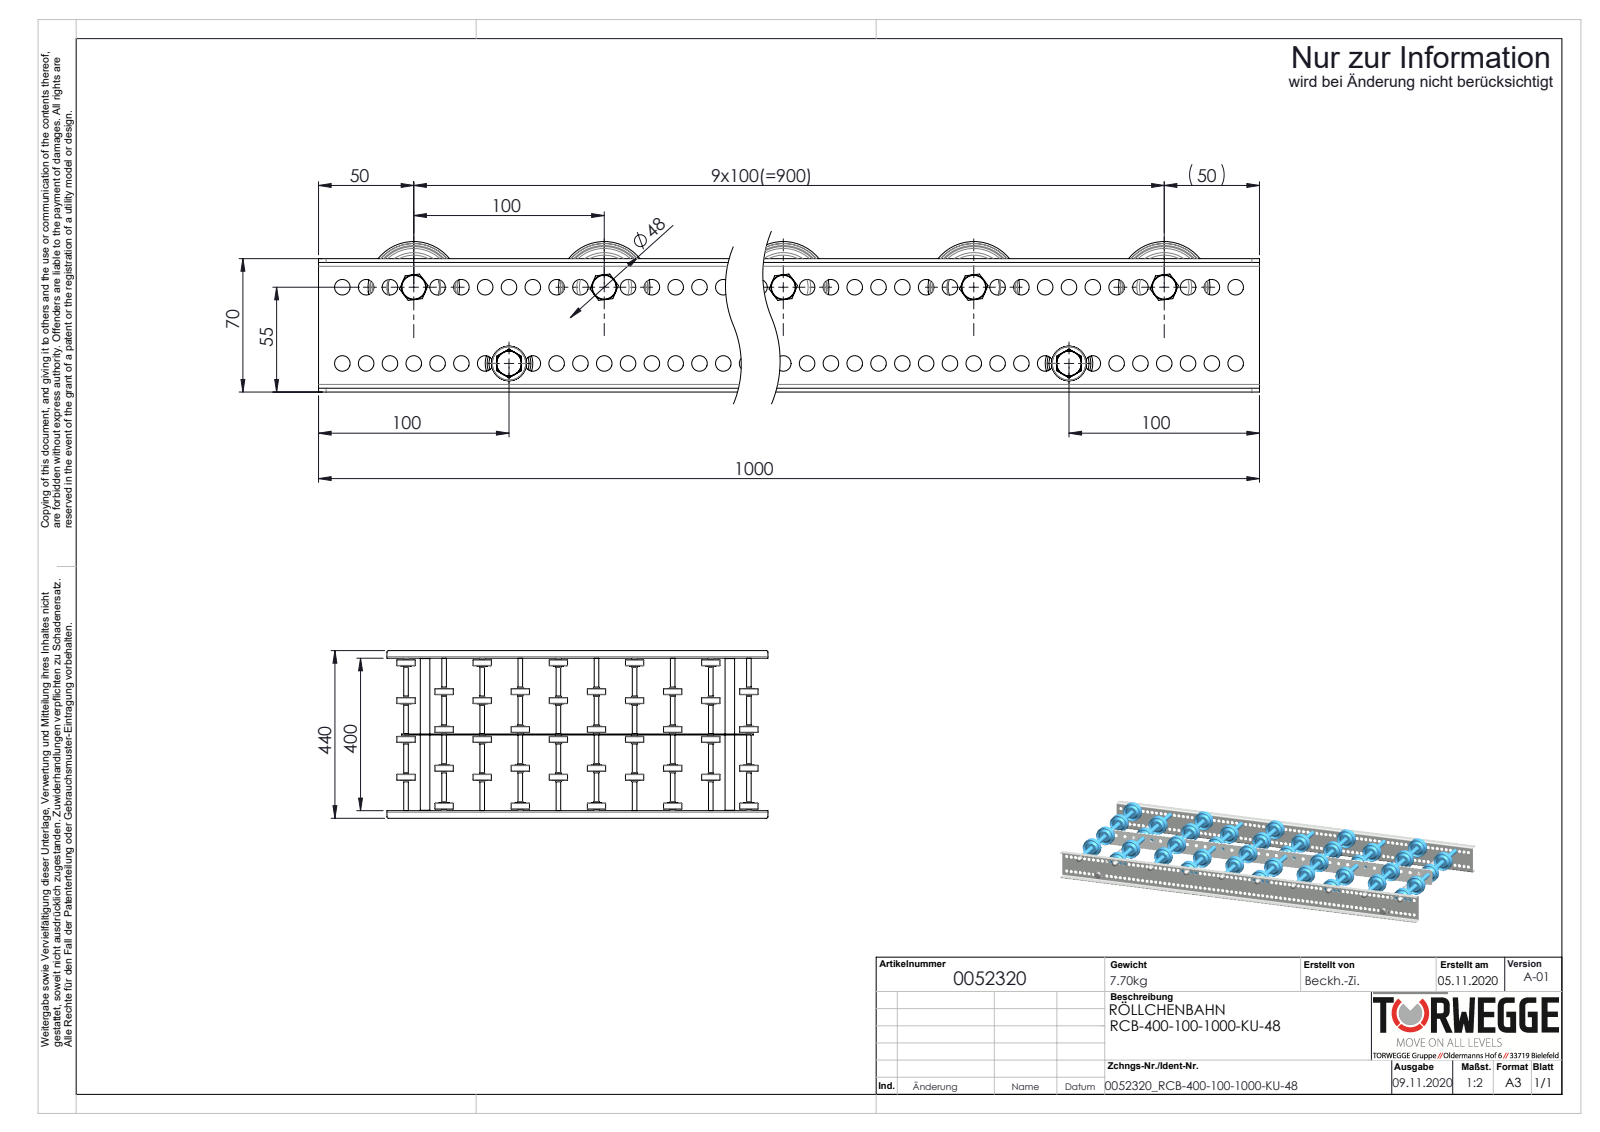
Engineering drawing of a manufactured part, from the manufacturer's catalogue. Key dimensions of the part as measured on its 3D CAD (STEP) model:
Part name (STEP PRODUCT): S100994_Sperrzahnschraube_M08x16-8.8-A2K; S100100_Längstraverse-42x2,5_S100101_Lngstraverse-RB-L975; Röllchenachse-für-Konfiguration_EL400; Traversen_KFG_L400 (+6 more)
STEP written by: SolidWorks 2020 (AUTOMOTIVE_DESIGN)
Units: millimetres
Bodies: 123 solids, 4636 faces (826 planar, 1746 cylindrical, 2064 other)
Overall size (bounding box): 1000 × 440 × 79
Volume: 1 729 000 mm³ · Surface area: 1 330 000 mm²
Round holes (diameter × count): ⌀8.2 ×158, ⌀8.5 ×37, ⌀6.65 ×10, ⌀9.65 ×10, ⌀13.7 ×10, ⌀6.8 ×2, ⌀21 ×2
Round bosses / shafts (diameter × count): ⌀8 ×12, ⌀48 ×10, ⌀27 ×10, ⌀12.7 ×10, ⌀12.5 ×10, ⌀12 ×10, ⌀25 ×2
Partial cylindrical surfaces — rounded edges, fillets, slot ends (radius × count): R4 ×8, R2 ×4, R5 ×4
Main face-to-face distances: 2, 402, 68, 404, 400, 201.1, 198.6, 200.9, 198.9, 203.1
Hole centre spacings: 12.5, 25, 37.5, 50, 62.5, 75, 87.5, 100
